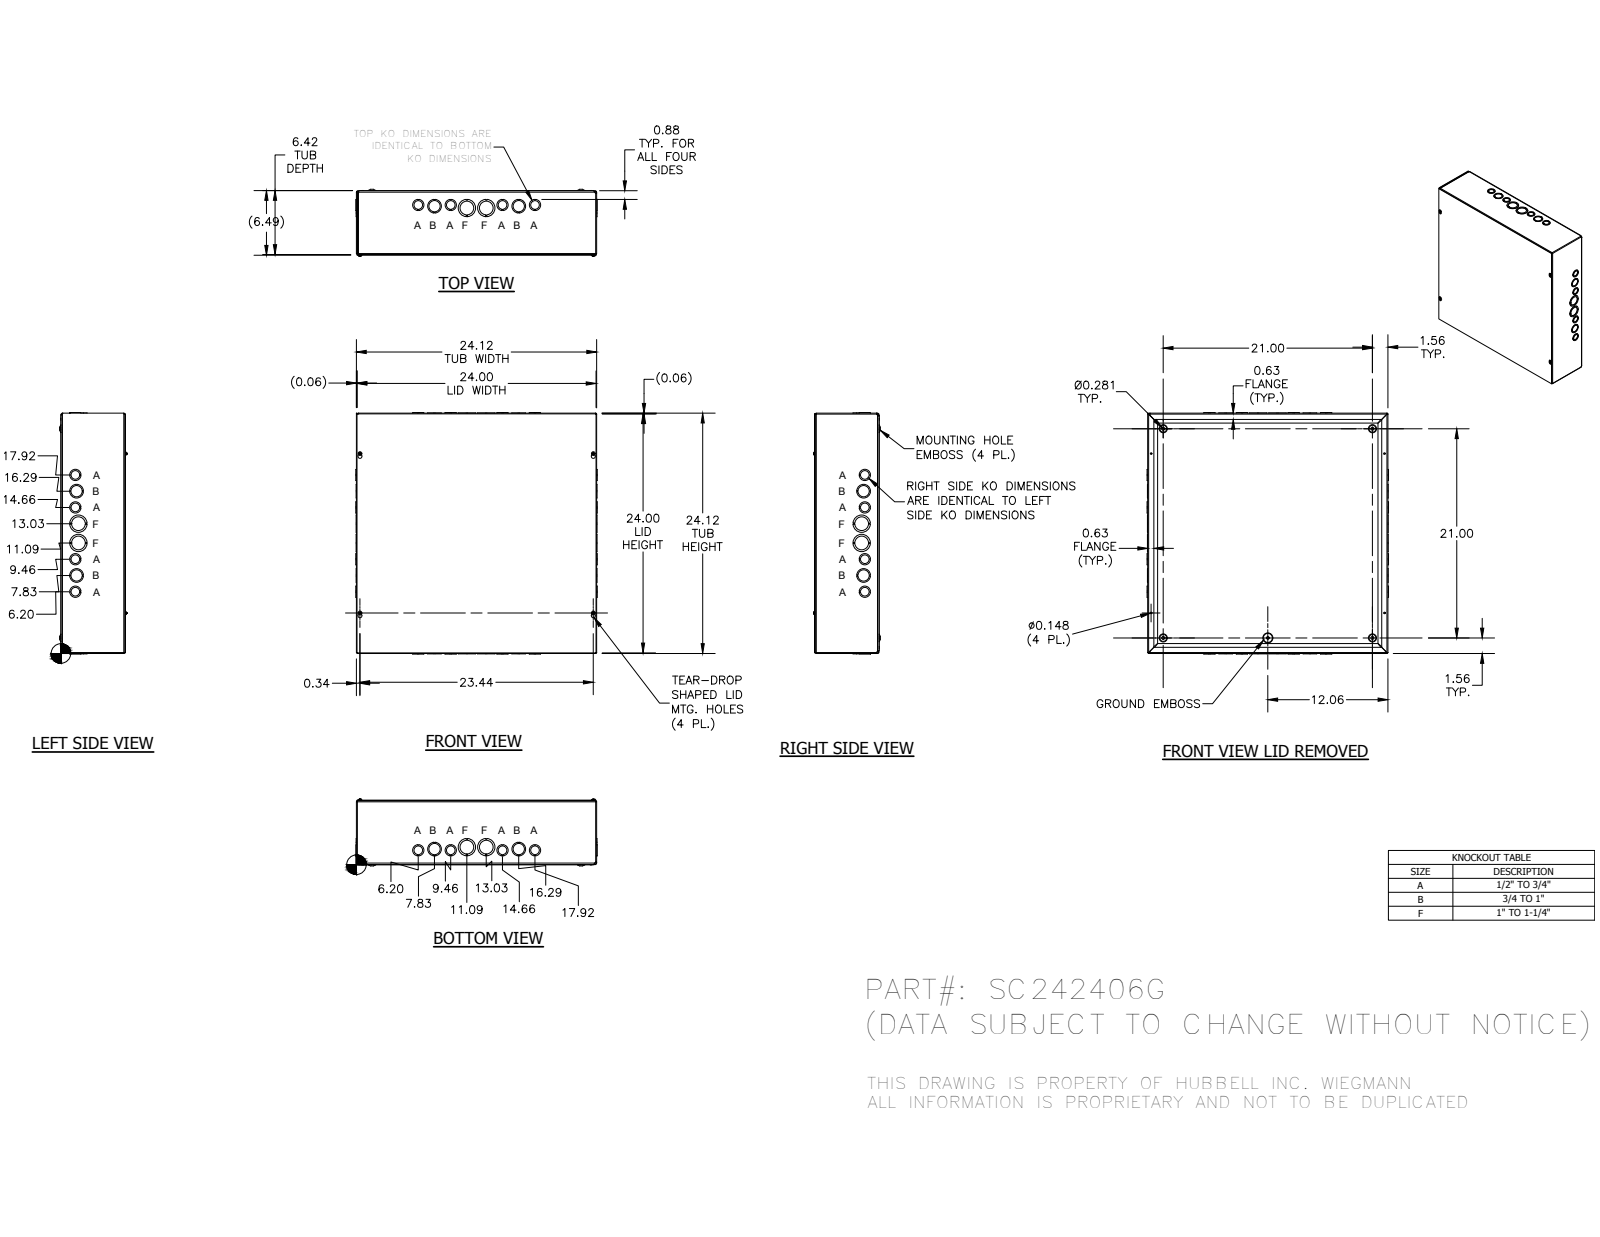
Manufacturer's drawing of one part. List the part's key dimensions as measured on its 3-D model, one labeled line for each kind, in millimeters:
Part name (STEP PRODUCT): SC2424GBKP; SC242406GWRA; SC2424GLID; 34056 (+1 more)
STEP written by: Autodesk Inventor 2014 (AUTOMOTIVE_DESIGN)
Units: millimetres
Bodies: 38 solids, 1255 faces (839 planar, 273 cylindrical, 143 other)
Overall size (bounding box): 615.92 × 615.92 × 170.59
Round holes (diameter × count): ⌀28.57 ×12, ⌀22.22 ×8, ⌀34.92 ×8, ⌀3.76 ×4, ⌀7.62 ×4, ⌀44.45 ×4, ⌀4.19 ×1
Round bosses / shafts (diameter × count): ⌀4.57 ×8, ⌀9.75 ×4, ⌀4.17 ×4, ⌀5.8 ×1
Partial cylindrical surfaces — rounded edges, fillets, slot ends (radius × count): R0.79 ×8, R2.37 ×8, R1.4 ×4, R1.57 ×4, R2.38 ×4, R2.79 ×4, R2.97 ×4, R3.15 ×4
Main face-to-face distances: 1.88, 163, 161.12, 164.88, 1.57, 1.58, 612.78, 611.2, 611.21, 609.63
Hole centre spacings: 41.52, 42.15, 82.94, 91.03, 132.17, 173.51, 214.88, 470.92
